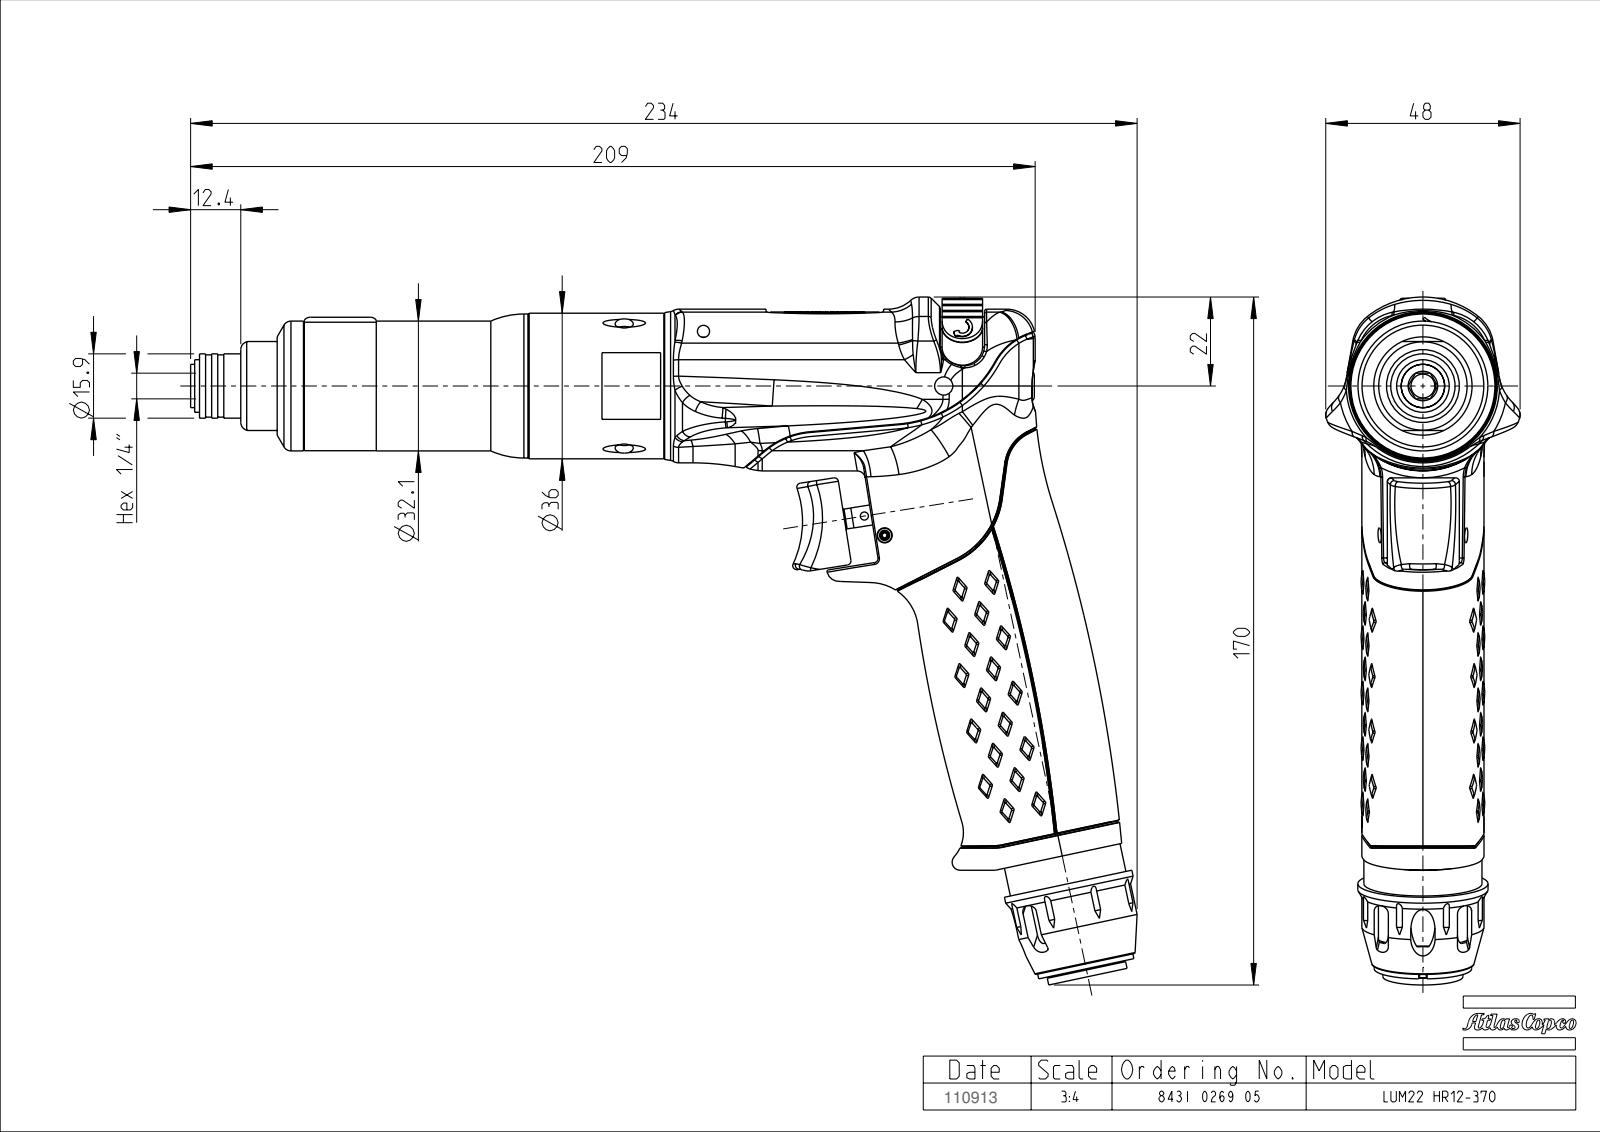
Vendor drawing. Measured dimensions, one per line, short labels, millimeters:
name: TMP15927_SW
written by: PRO/ENGINEER BY PARAMETRIC TECHNOLOGY CORPORATION, 2008310 (CONFIG_CONTROL_DESIGN)
unit: mm
bodies: 0 solids, 805 faces (90 planar, 164 cylindrical, 551 other)
size: 234.01 × 170.1 × 48.06
holes: 2× ⌀4.5, 1× ⌀3, 1× ⌀7.3, 1× ⌀7.5, 1× ⌀11.45, 1× ⌀26.4
bosses: 1× ⌀36, 1× ⌀35.6, 1× ⌀32.2, 1× ⌀32.1, 1× ⌀32, 1× ⌀30.2, 1× ⌀29.2, 1× ⌀24.25
rounds: 8× R0.75, 8× R1, 4× R10, 3× R38, 2× R1.5, 2× R2.5, 2× R3, 2× R5
face distances: 1.5, 29.8, 32, 1.2, 2, 27.29, 57.09, 3.2, 30.49, 60.29
